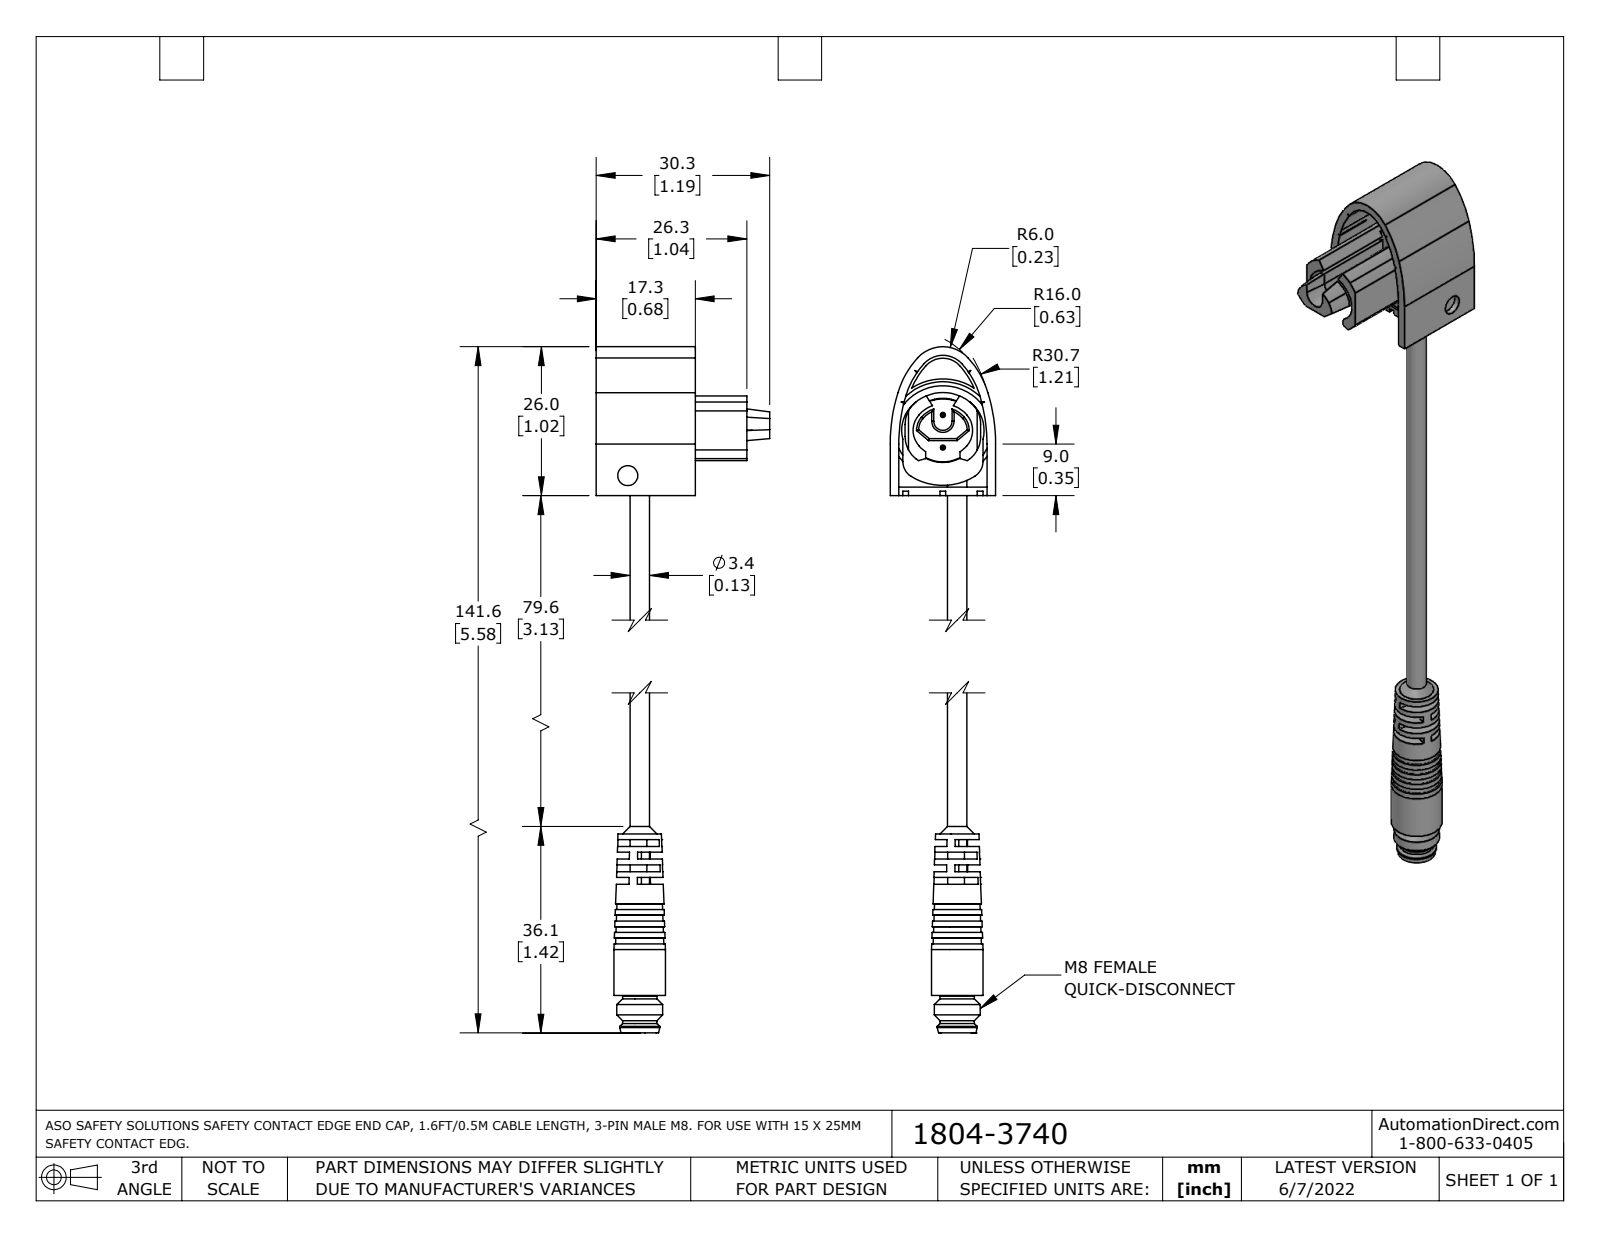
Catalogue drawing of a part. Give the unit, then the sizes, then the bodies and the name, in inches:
Units: inches
Overall size (bounding box): 5.579 × 1.193 × 0.724
Round holes (diameter × count): ⌀0.028 ×2, ⌀0.035 ×2, ⌀0.138 ×2, ⌀0.134 ×1, ⌀0.228 ×1
Round bosses / shafts (diameter × count): ⌀0.039 ×3, ⌀0.059 ×2, ⌀0.024 ×2, ⌀0.354 ×1, ⌀0.315 ×1, ⌀0.276 ×1, ⌀0.236 ×1
Partial cylindrical surfaces — rounded edges, fillets, slot ends (radius × count): R0.197 ×6, R0.039 ×4, R0.02 ×2, R0.118 ×2, R0.138 ×2, R0.161 ×2, R0.201 ×2, R0.219 ×2
Main face-to-face distances: 0.059, 0.126, 0.665, 0.087, 0.173, 0.047, 0.039, 0.299, 0.598, 0.067
Hole centre spacings: 0.128, 0.224
Volume: 0.443 in³ · Surface area: 14.4 in²
Bodies: 11 solids, 306 faces (154 planar, 103 cylindrical, 49 other)
Part name (STEP PRODUCT): 1804-3740
STEP written by: SolidWorks 2018 (AUTOMOTIVE_DESIGN)
